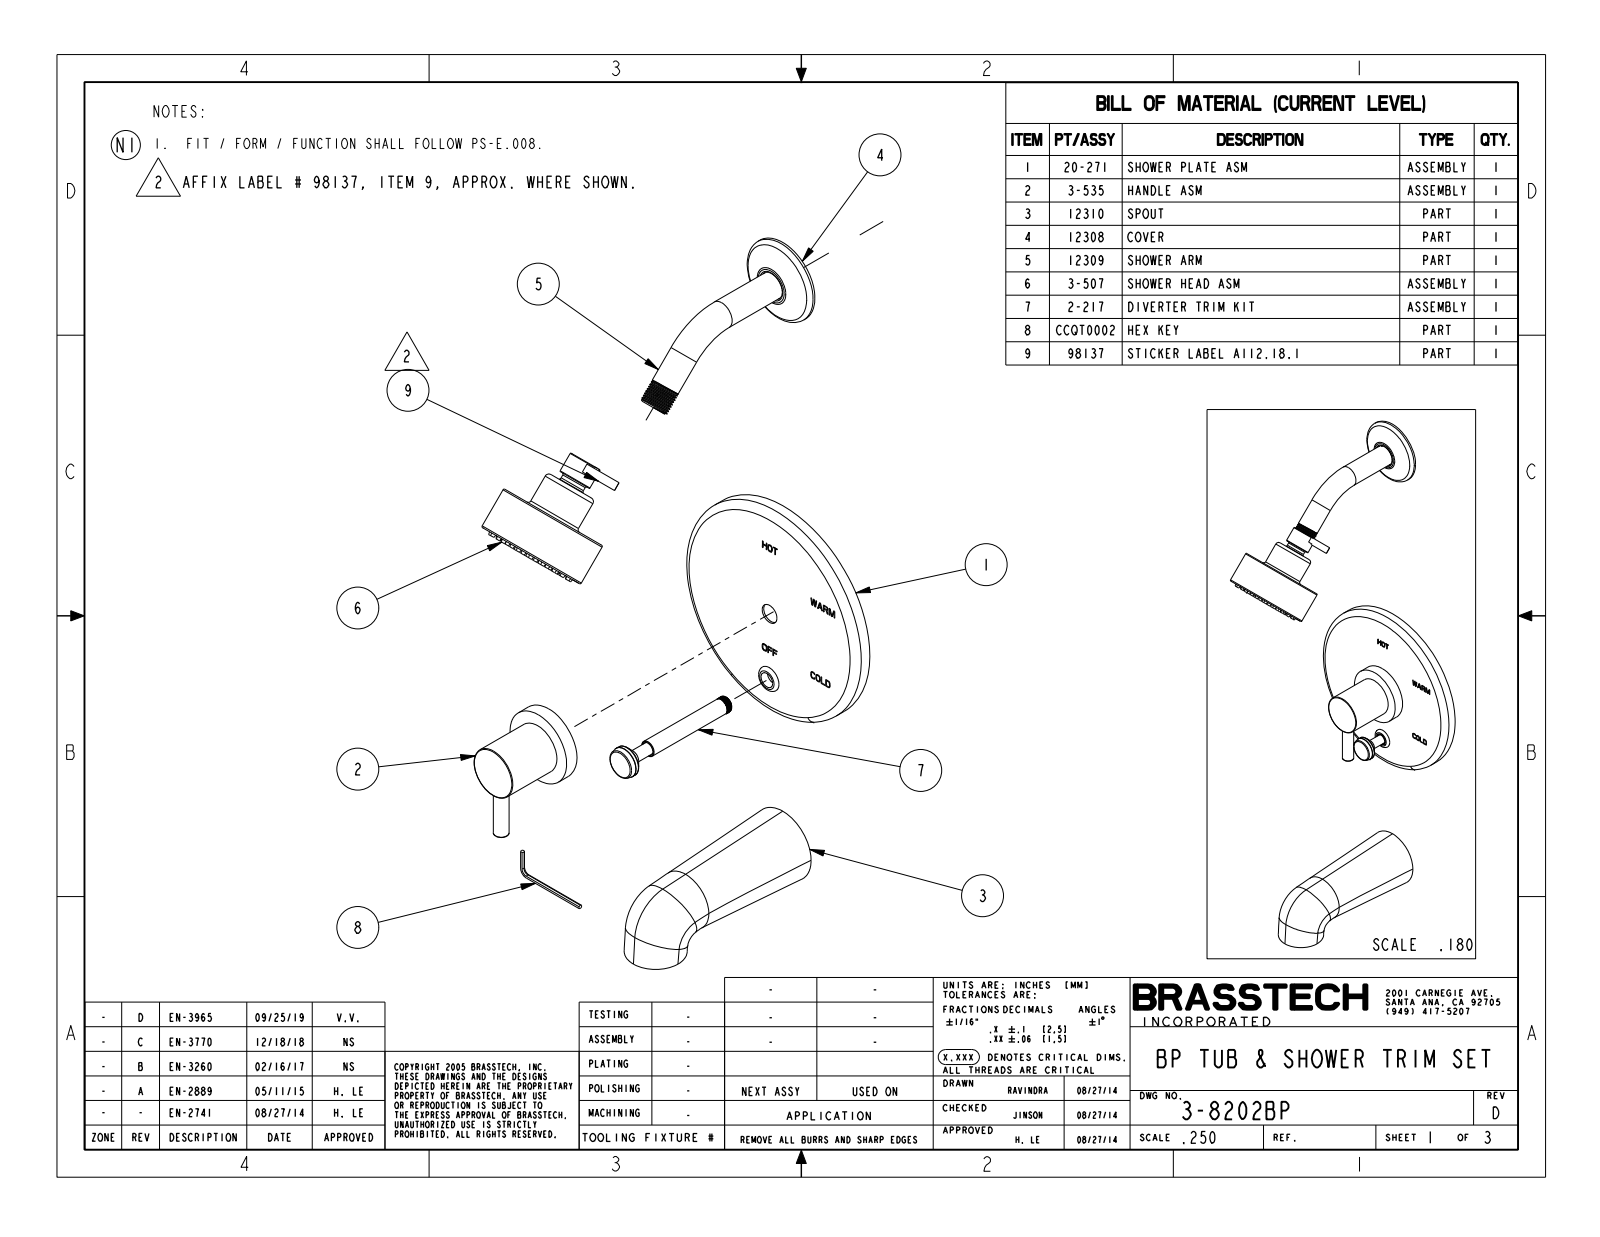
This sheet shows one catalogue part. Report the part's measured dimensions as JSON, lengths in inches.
{"part_name": "CTCB-026_1_AF0; CTWR_1_AF0; 91033_1; 3-505_AF0_ASM (+8 more)", "step_written_by": "PRO/ENGINEER BY PARAMETRIC TECHNOLOGY CORPORATION, 2013150 (CONFIG_CONTROL_DESIGN)", "units": "inches", "bodies": {"solids": 20, "faces": 1599, "planar": 642, "cylindrical": 513, "other": 444}, "overall_size": [21.392, 10.354, 6.693], "volume_in3": 21.5, "surface_area_in2": 335.8, "round_holes": [[0.039, 48], [0.315, 2], [0.685, 2], [0.15, 1], [0.156, 1], [0.165, 1], [0.256, 1], [0.265, 1], [0.318, 1], [0.335, 1], [0.345, 1], [0.399, 1]], "round_bosses_or_shafts": [[0.811, 2], [0.236, 2], [6.693, 1], [6.593, 1], [3.15, 1], [2.5, 1], [2.2, 1], [1.969, 1]], "partial_cylinders_radius": [[0.004, 30], [0.03, 18], [0.015, 15], [0.016, 6], [0.039, 5], [0.059, 5], [0.016, 2], [0.118, 2]], "face_to_face_distances": [0.354, 1.22, 0.597, 0.951, 0.06, 0.537, 0.891, 0.354, 0.951, 0.891], "hole_center_spacings": [0.752, 1.002, 1.003, 1.063, 1.302, 1.418, 1.967, 0.391]}
